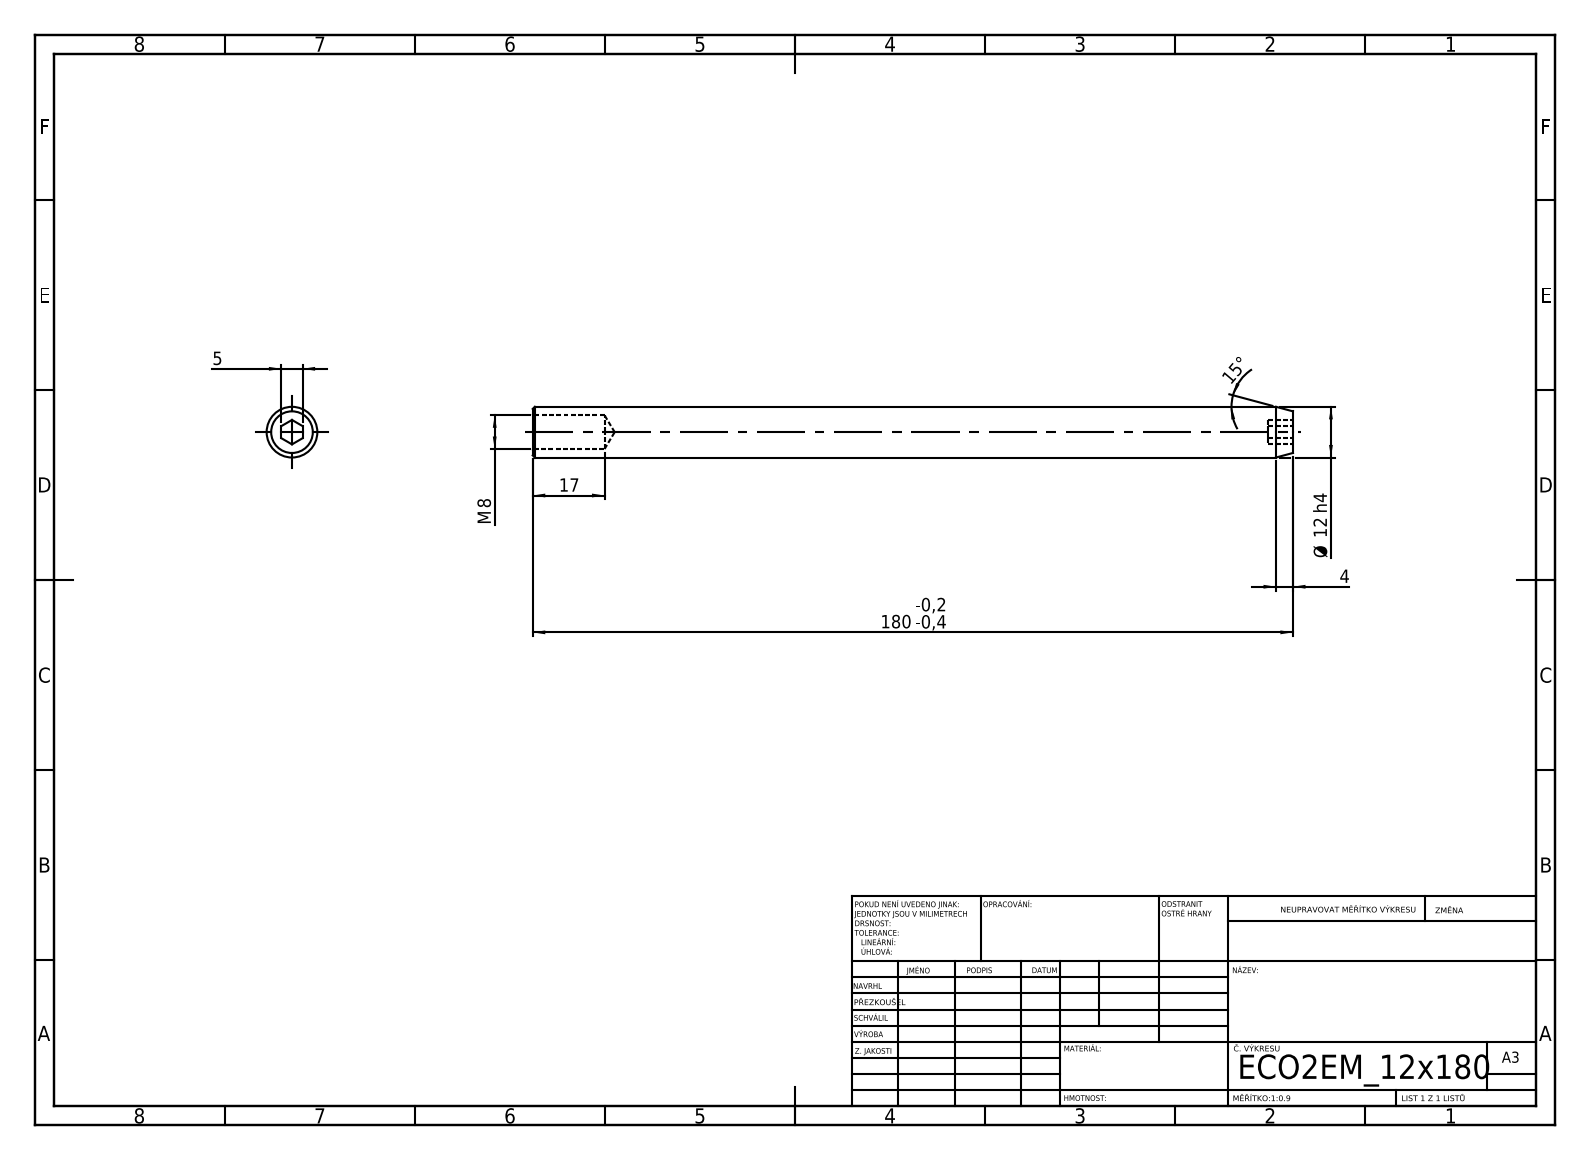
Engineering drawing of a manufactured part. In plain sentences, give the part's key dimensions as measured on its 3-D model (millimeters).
Its 3-D file was written by "SolidWorks 2019 (CONFIG_CONTROL_DESIGN)". It is 1 solid with 21 faces: 9 planar, 4 cylindrical and 8 other. Overall it measures 180 by 12 by 12 millimeters. Its volume is 19 256 cubic millimeters and its surface area 7 488 square millimeters. Round holes: 1 of diameter 8. Round bosses or shafts: 1 of diameter 12. The main face-to-face distances are 5, 180, 5.8, 174.2.
